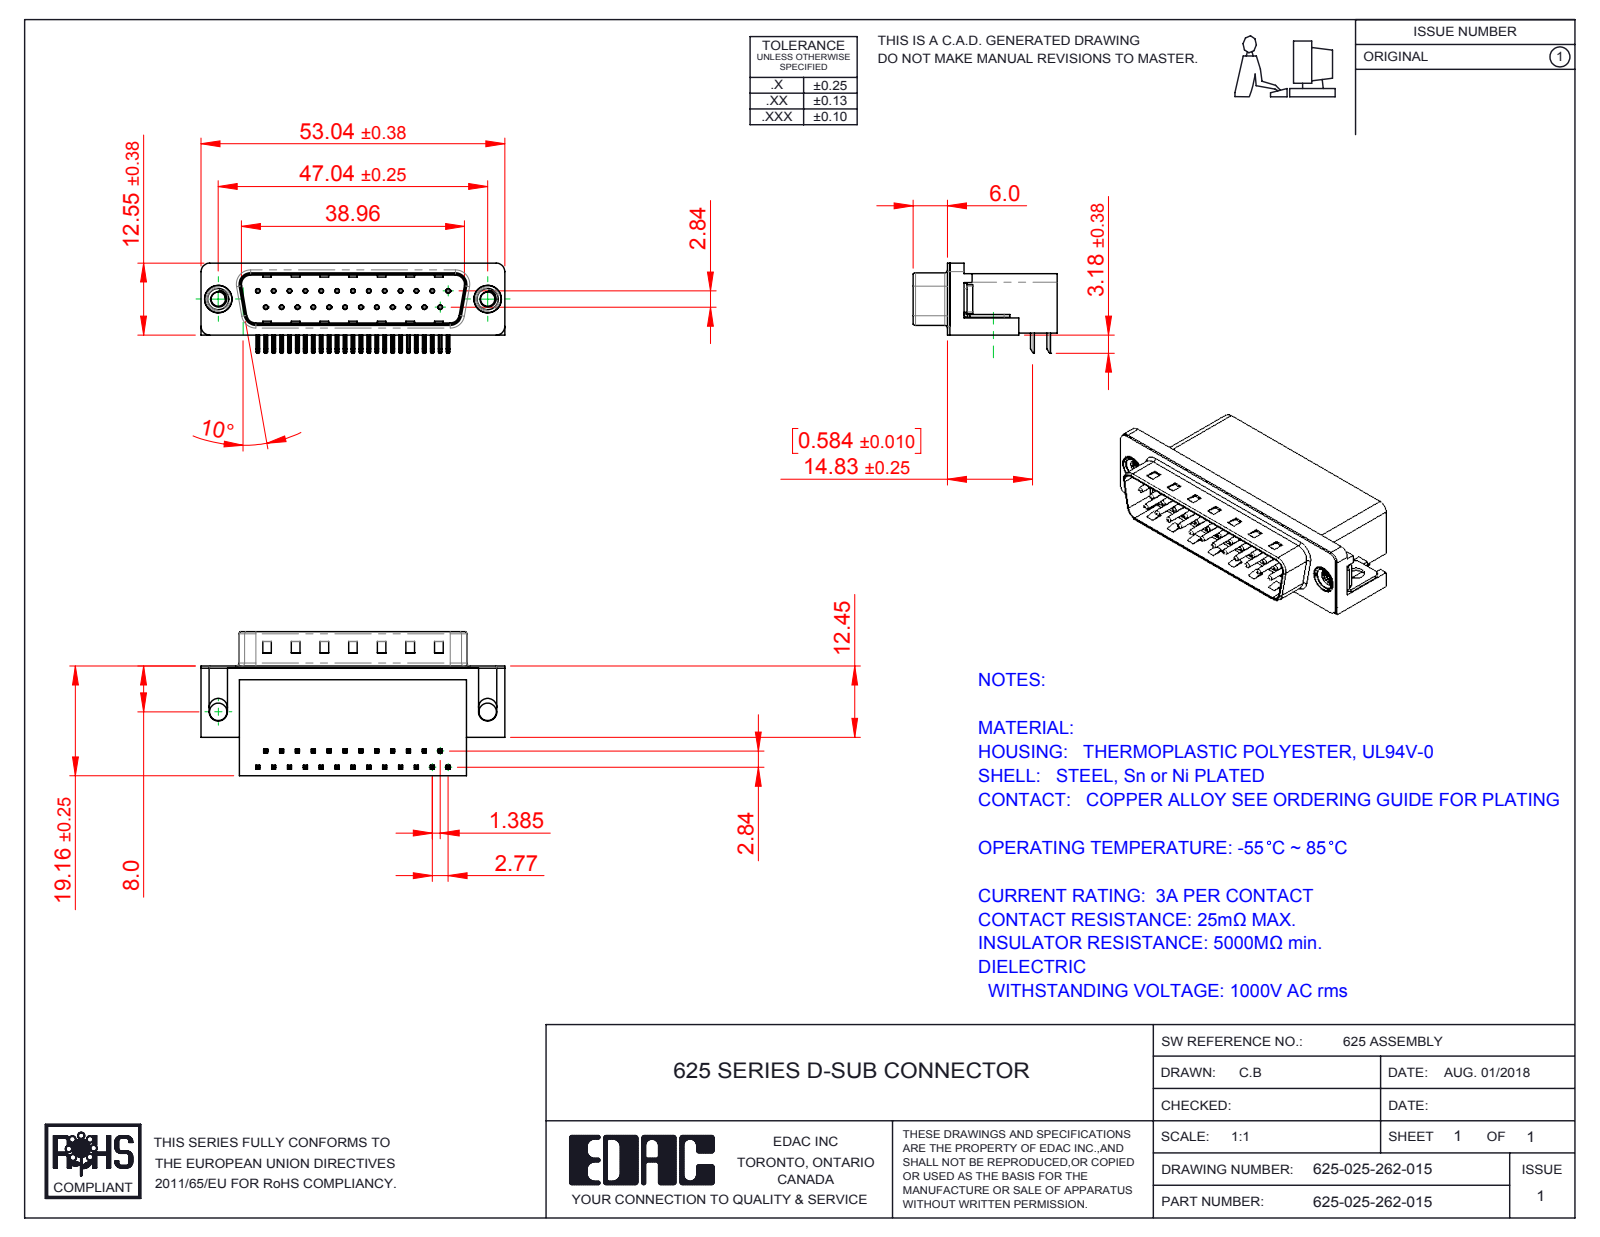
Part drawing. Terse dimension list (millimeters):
name: 625 Contact Top; 625-025-262-015; 625 Shell_25 Socket; 625 Thru Hole Board Mount (+3 more)
written by: SolidWorks 2016 (CONFIG_CONTROL_DESIGN)
unit: mm
bodies: 31 solids, 2265 faces (1405 planar, 665 cylindrical, 195 other)
size: 53.04 × 25.16 × 15.73
volume: 9 157 mm³; area: 8 852 mm²
holes: 25× ⌀0.35, 25× ⌀0.8, 2× ⌀2.5, 2× ⌀3.05, 2× ⌀4, 2× ⌀4.8, 2× ⌀5
bosses: 25× ⌀0.75, 2× ⌀4.9, 2× ⌀4.75, 2× ⌀3.9
rounds: 108× R0.25, 50× R0.12, 16× R1, 9× R0.5, 8× R1.6, 7× R1.5, 4× R0.9, 4× R2
face distances: 0.4, 10.35, 18.76, 2.1, 8.76, 10.46, 10.86, 1.7, 19.16, 10.11
hole spacings: 3.16, 2.77, 11.08, 5.54, 8.31, 5.03, 13.85, 7.48
